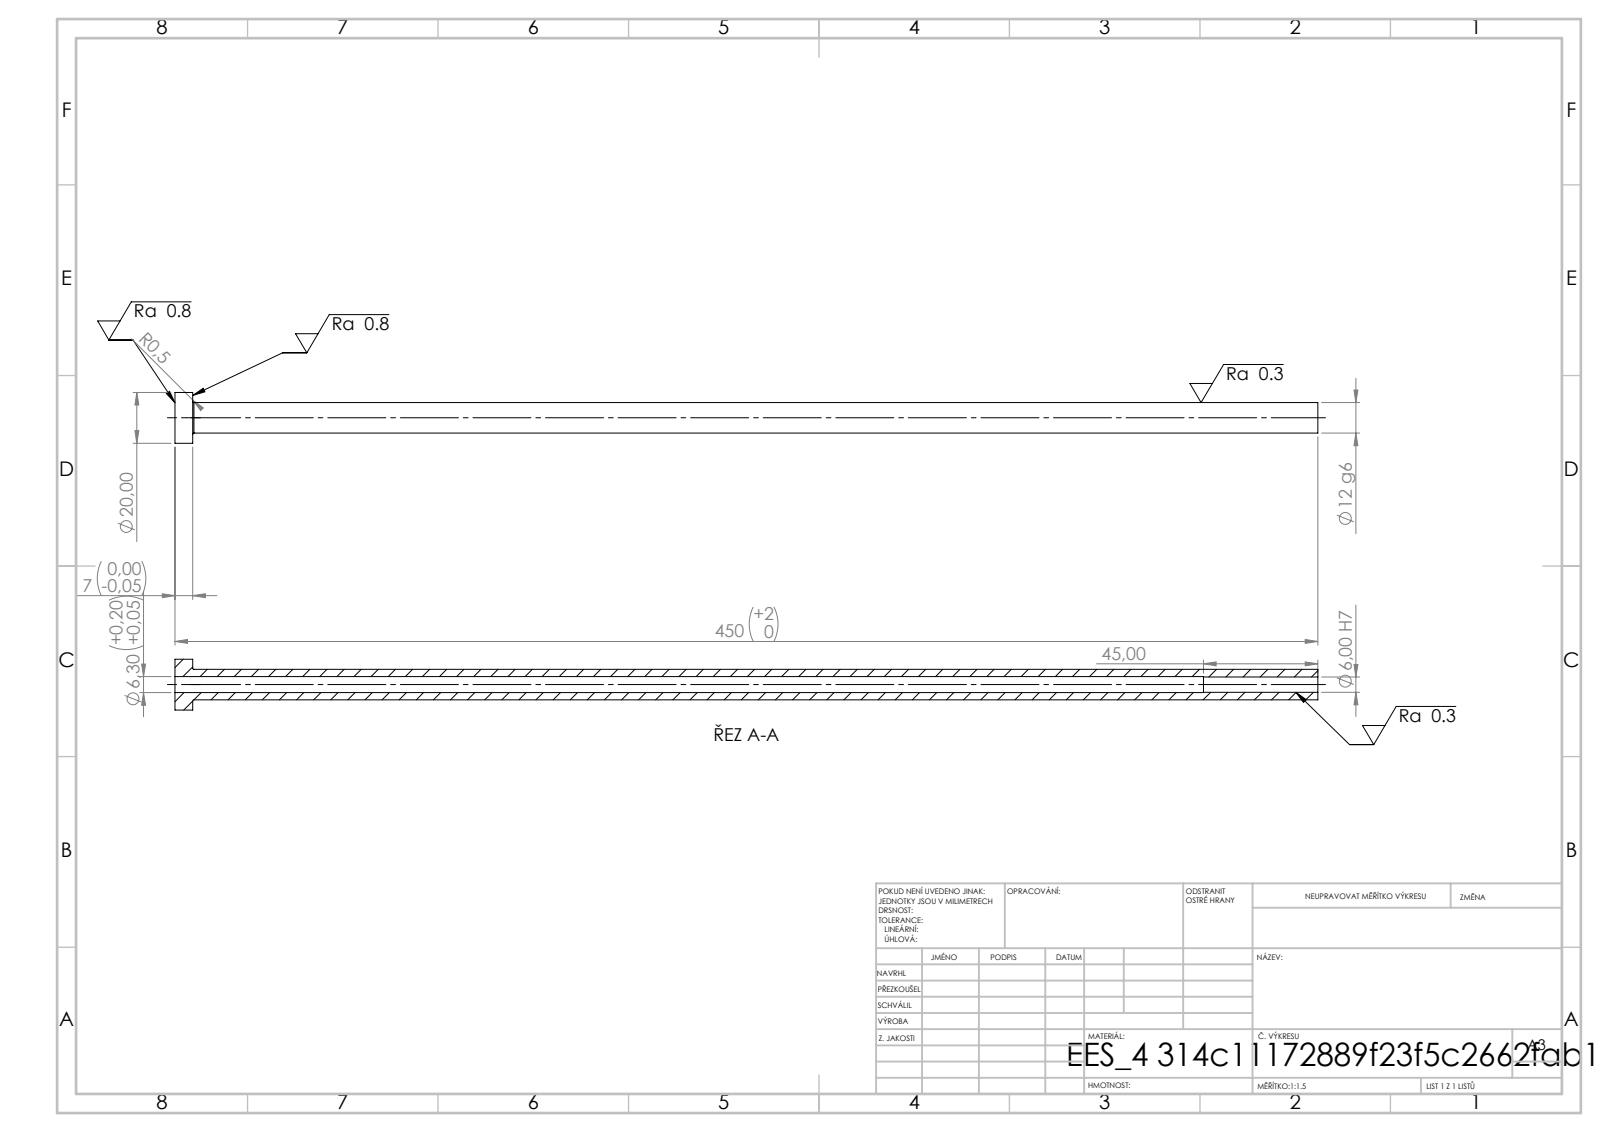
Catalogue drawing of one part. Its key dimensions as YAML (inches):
step_written_by: "SolidWorks 2019 (CONFIG_CONTROL_DESIGN)"
units: inches
bodies: {solids: 1, faces: 14, planar: 4, cylindrical: 8, other: 2}
overall_size: [17.717, 0.787, 0.787]
volume: 2.344
surface_area: 41.18
round_holes:
  - {diameter: 0.236, count: 1}
  - {diameter: 0.248, count: 1}
round_bosses_or_shafts:
  - {diameter: 0.787, count: 1}
  - {diameter: 0.472, count: 1}
face_to_face_distances: [0.276, 17.717, 17.441, 15.945, 15.669, 1.772]
